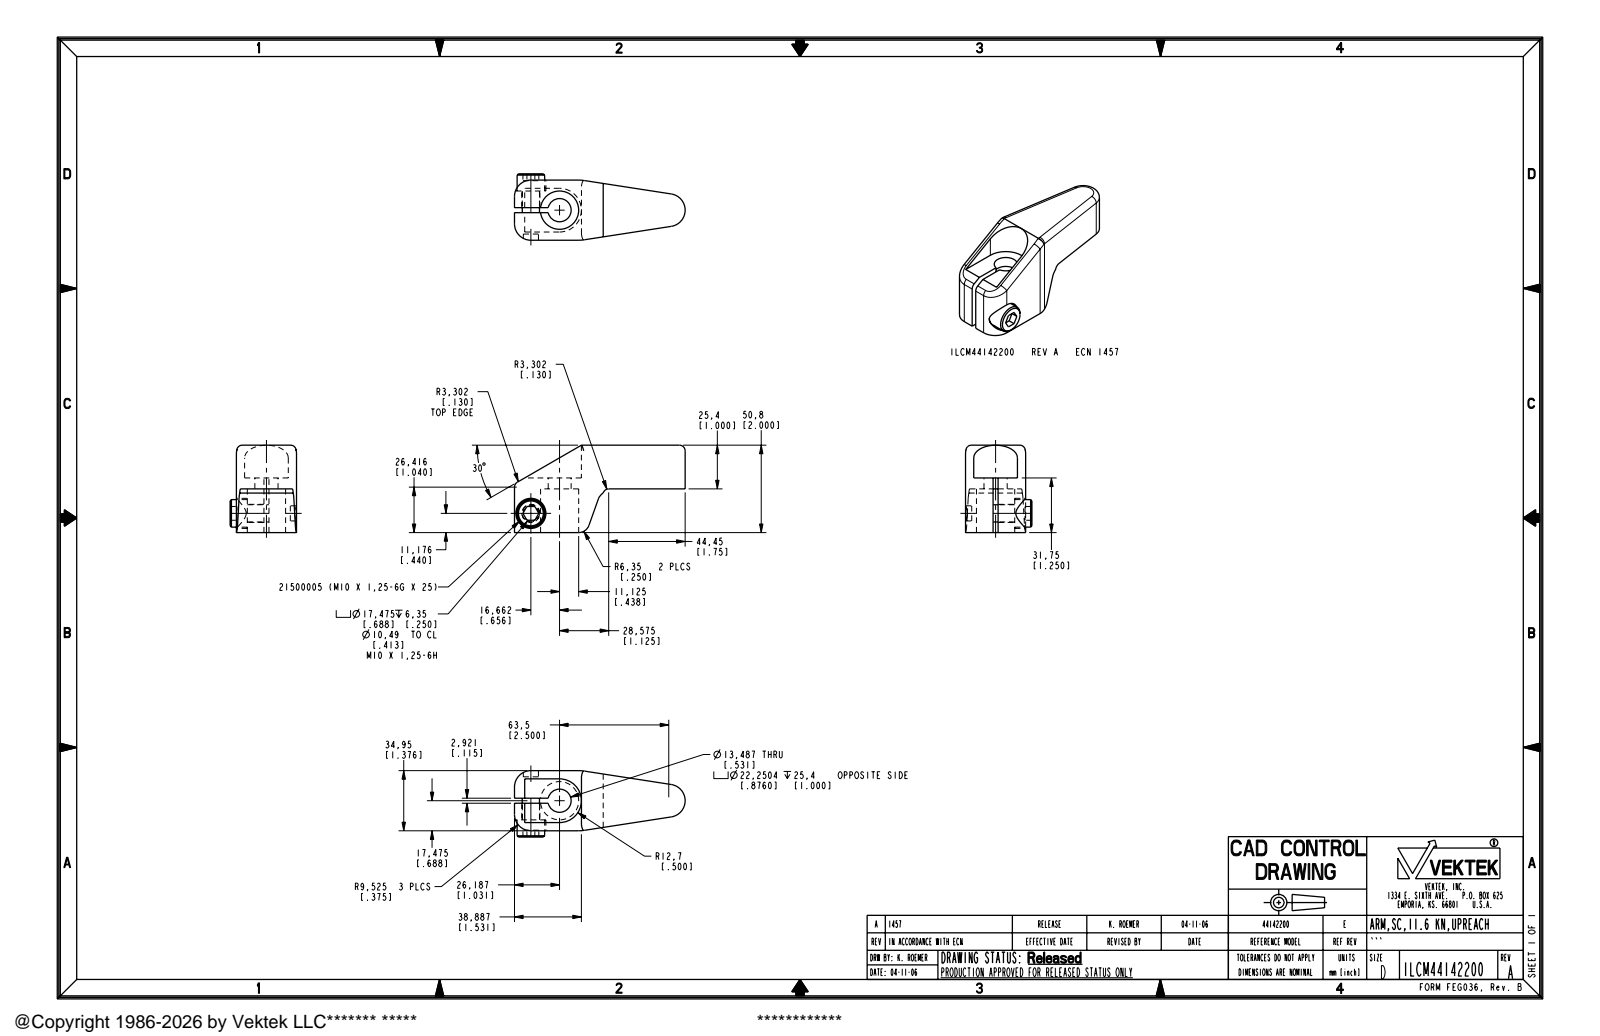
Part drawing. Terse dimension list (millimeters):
name: ILCM44142200
written by: PRO/ENGINEER BY PARAMETRIC TECHNOLOGY CORPORATION, 2004290 (AUTOMOTIVE_DESIGN_CC2)
unit: mm
bodies: 1 solid, 67 faces (29 planar, 29 cylindrical, 9 other)
size: 99.21 × 50.8 × 38.6
volume: 78 456 mm³; area: 18 402 mm²
holes: 1× ⌀8.79, 1× ⌀10.49, 1× ⌀13.49, 1× ⌀17.48, 1× ⌀22.25
bosses: 1× ⌀16, 1× ⌀10
rounds: 8× R3.3, 3× R9.53, 2× R6.35, 2× R25.4, 1× R12.7
face distances: 25.4, 34.96, 16.02, 18.94, 50.8, 19.05, 6.35, 31.75, 2.92, 4.78
